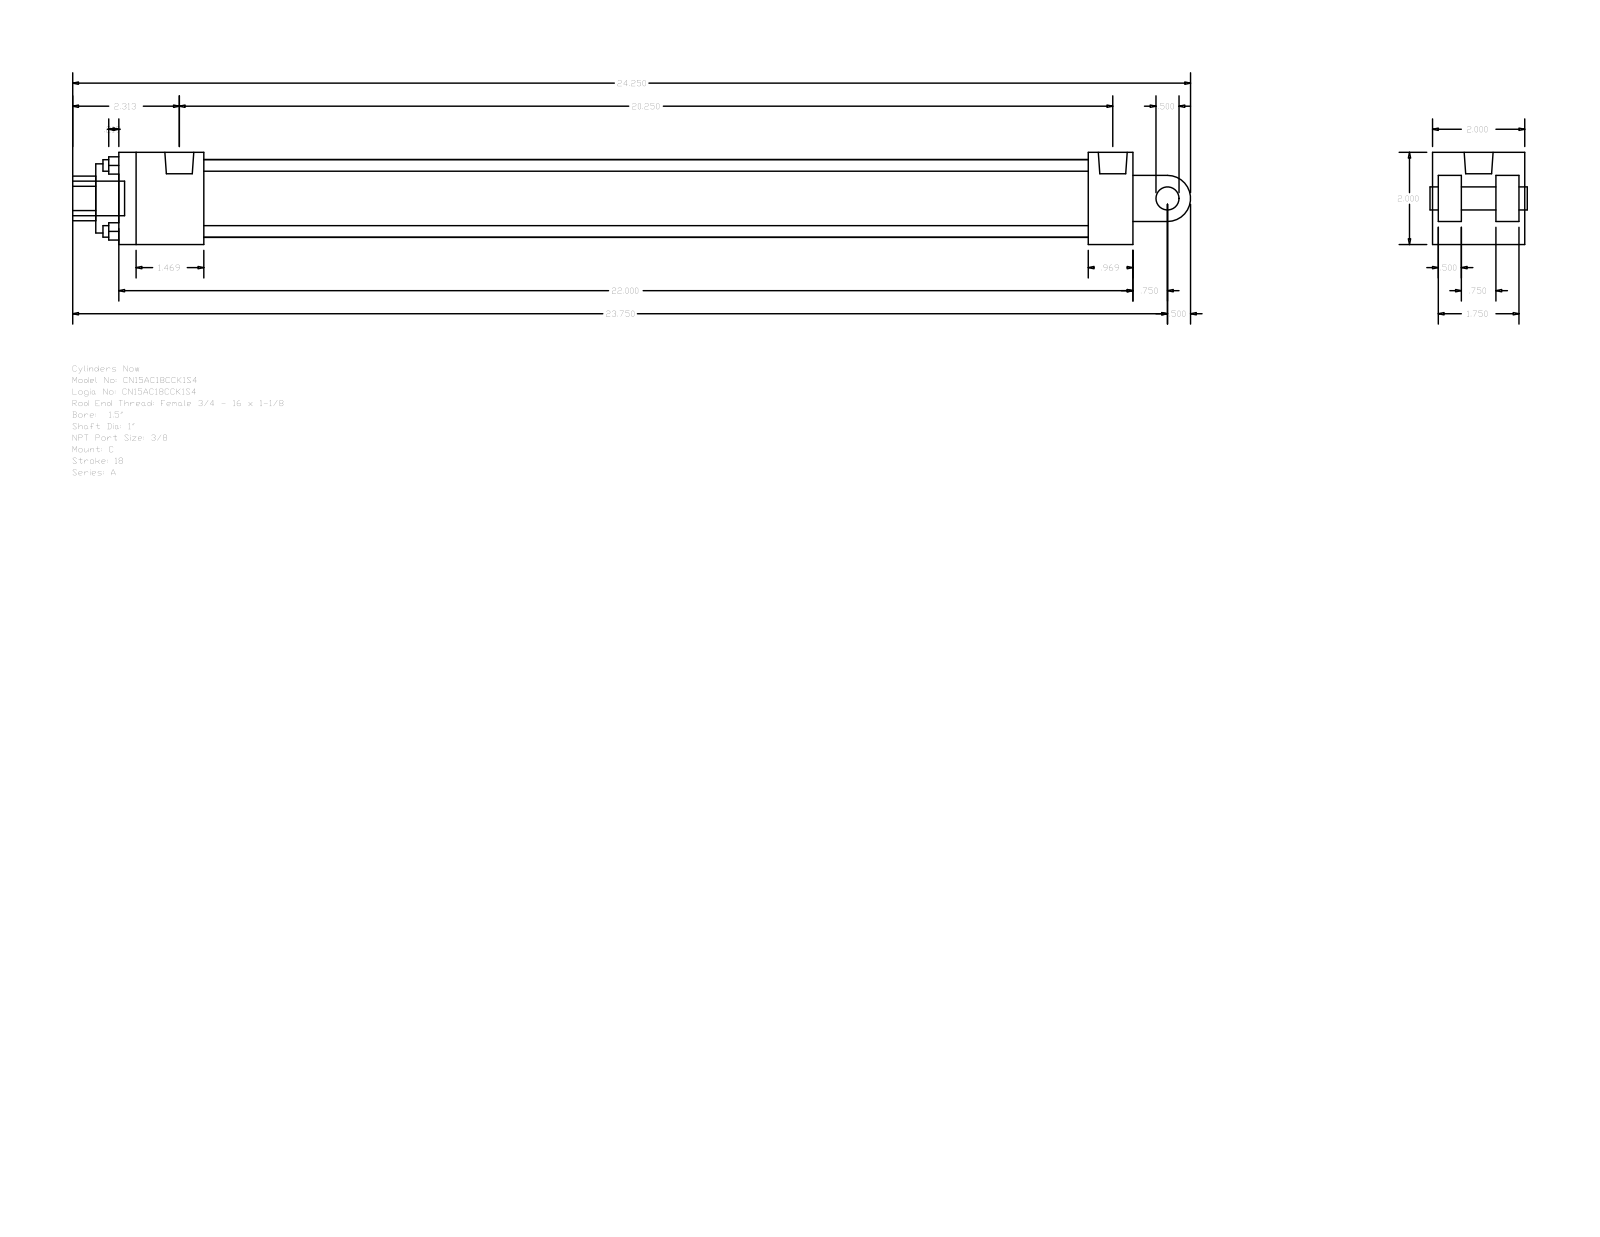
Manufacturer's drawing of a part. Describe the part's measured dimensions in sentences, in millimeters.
The part is named "A_C__0150_1". Its 3-D file was written by "GSSL Pune (CONFIG_CONTROL_DESIGN)". It is 0 solids with 99 faces: 70 planar, 29 cylindrical and 0 other. Overall it measures 615.95 by 50.8 by 50.8 millimeters. Round holes: 4 of diameter 6.35, 2 of diameter 5.56, 1 of diameter 15.93, 1 of diameter 25.4, 1 of diameter 38.1, 1 of diameter 42.93. Round bosses or shafts: 2 of diameter 5.56, 1 of diameter 19.05, 1 of diameter 15.93, 1 of diameter 12.7. Partial cylindrical surfaces (rounded edges, fillets, slot ends): 1 of radius 12.29, 1 of radius 12.7. The main face-to-face distances are 50.8, 12.7, 3.17, 15.87, 47.63, 34.93, 31.76, 558.8, 534.19, 24.61. The hole center spacings are 25.68, 36.32, 51.36, 3.97.
